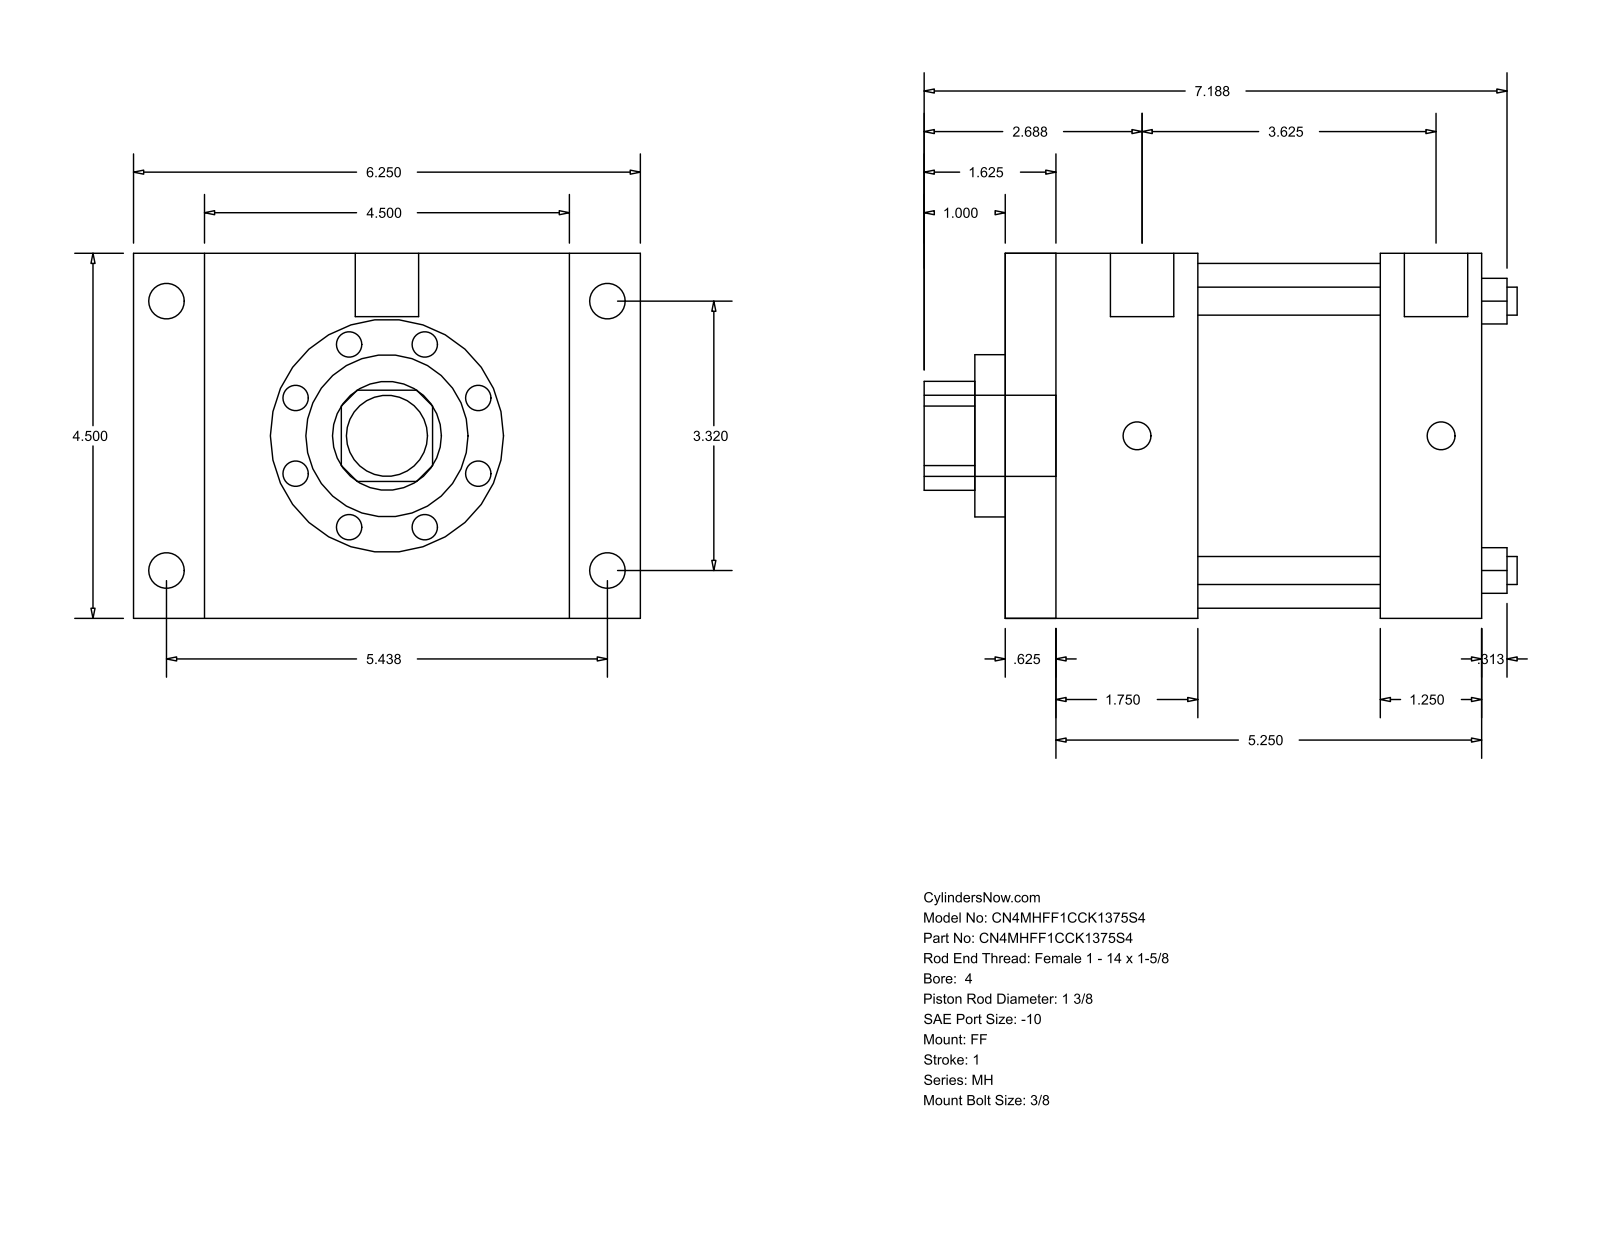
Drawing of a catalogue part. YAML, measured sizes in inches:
part_name: "MH_FF__0400_1.375"
step_written_by: "GSSL Pune (CONFIG_CONTROL_DESIGN)"
units: inches
bodies: {solids: 0, faces: 92, planar: 64, cylindrical: 28, other: 0}
overall_size: [7.313, 6.25, 4.5]
round_holes:
  - {diameter: 0.345, count: 4}
  - {diameter: 1.375, count: 1}
  - {diameter: 2, count: 1}
  - {diameter: 4.25, count: 1}
round_bosses_or_shafts:
  - {diameter: 0.438, count: 4}
  - {diameter: 0.344, count: 4}
  - {diameter: 0.781, count: 2}
  - {diameter: 1, count: 1}
partial_cylinders:
  - {radius: 0.672, count: 1}
face_to_face_distances: [4.5, 5.875, 0.625, 5.25, 2.375, 1.75, 3.5, 4.625, 4, 2.25]
hole_center_spacings: [2.347, 3.32, 4.695]
